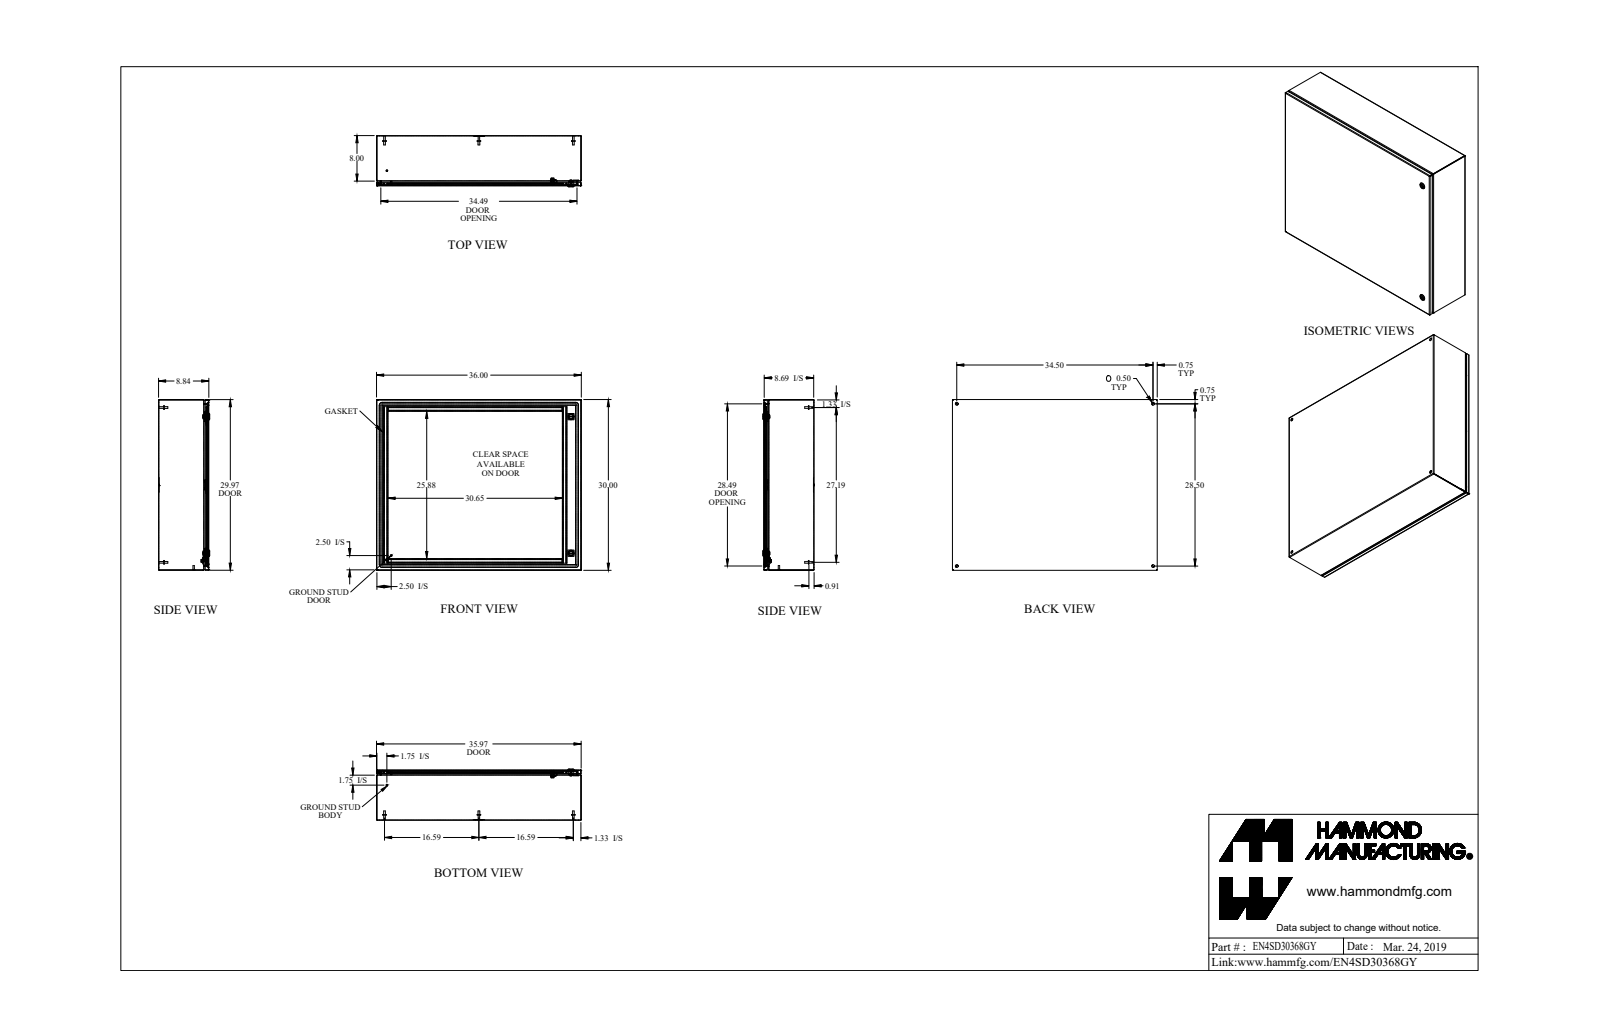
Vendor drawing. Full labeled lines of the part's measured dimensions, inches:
Part name (STEP PRODUCT): EN4SD30368GY_Default
STEP written by: SolidWorks 2019 (CONFIG_CONTROL_DESIGN)
Units: inches
Bodies: 39 solids, 1153 faces (547 planar, 383 cylindrical, 223 other)
Overall size (bounding box): 36 × 30 × 8.997
Volume: 272 in³ · Surface area: 7 698 in²
Round holes (diameter × count): ⌀0.5 ×4, ⌀0.232 ×2, ⌀0.625 ×2, ⌀0.785 ×2, ⌀0.172 ×1, ⌀0.196 ×1, ⌀0.24 ×1, ⌀0.242 ×1, ⌀0.275 ×1, ⌀0.375 ×1
Round bosses / shafts (diameter × count): ⌀0.625 ×7, ⌀0.313 ×6, ⌀0.27 ×6, ⌀1.1 ×2, ⌀0.525 ×2, ⌀0.281 ×2, ⌀0.25 ×2, ⌀0.455 ×1
Partial cylindrical surfaces — rounded edges, fillets, slot ends (radius × count): R0.043 ×24, R0.081 ×24, R0.036 ×20, R0.108 ×20, R0.062 ×14, R0.094 ×10, R0.312 ×10, R0.016 ×9
Main face-to-face distances: 0.072, 8.765, 8.693, 8.837, 29.928, 35.928, 29.856, 30, 35.856, 36
Hole centre spacings: 28.5, 33.503, 34.5, 44.749, 2.493, 2.494, 3.542, 4.441
